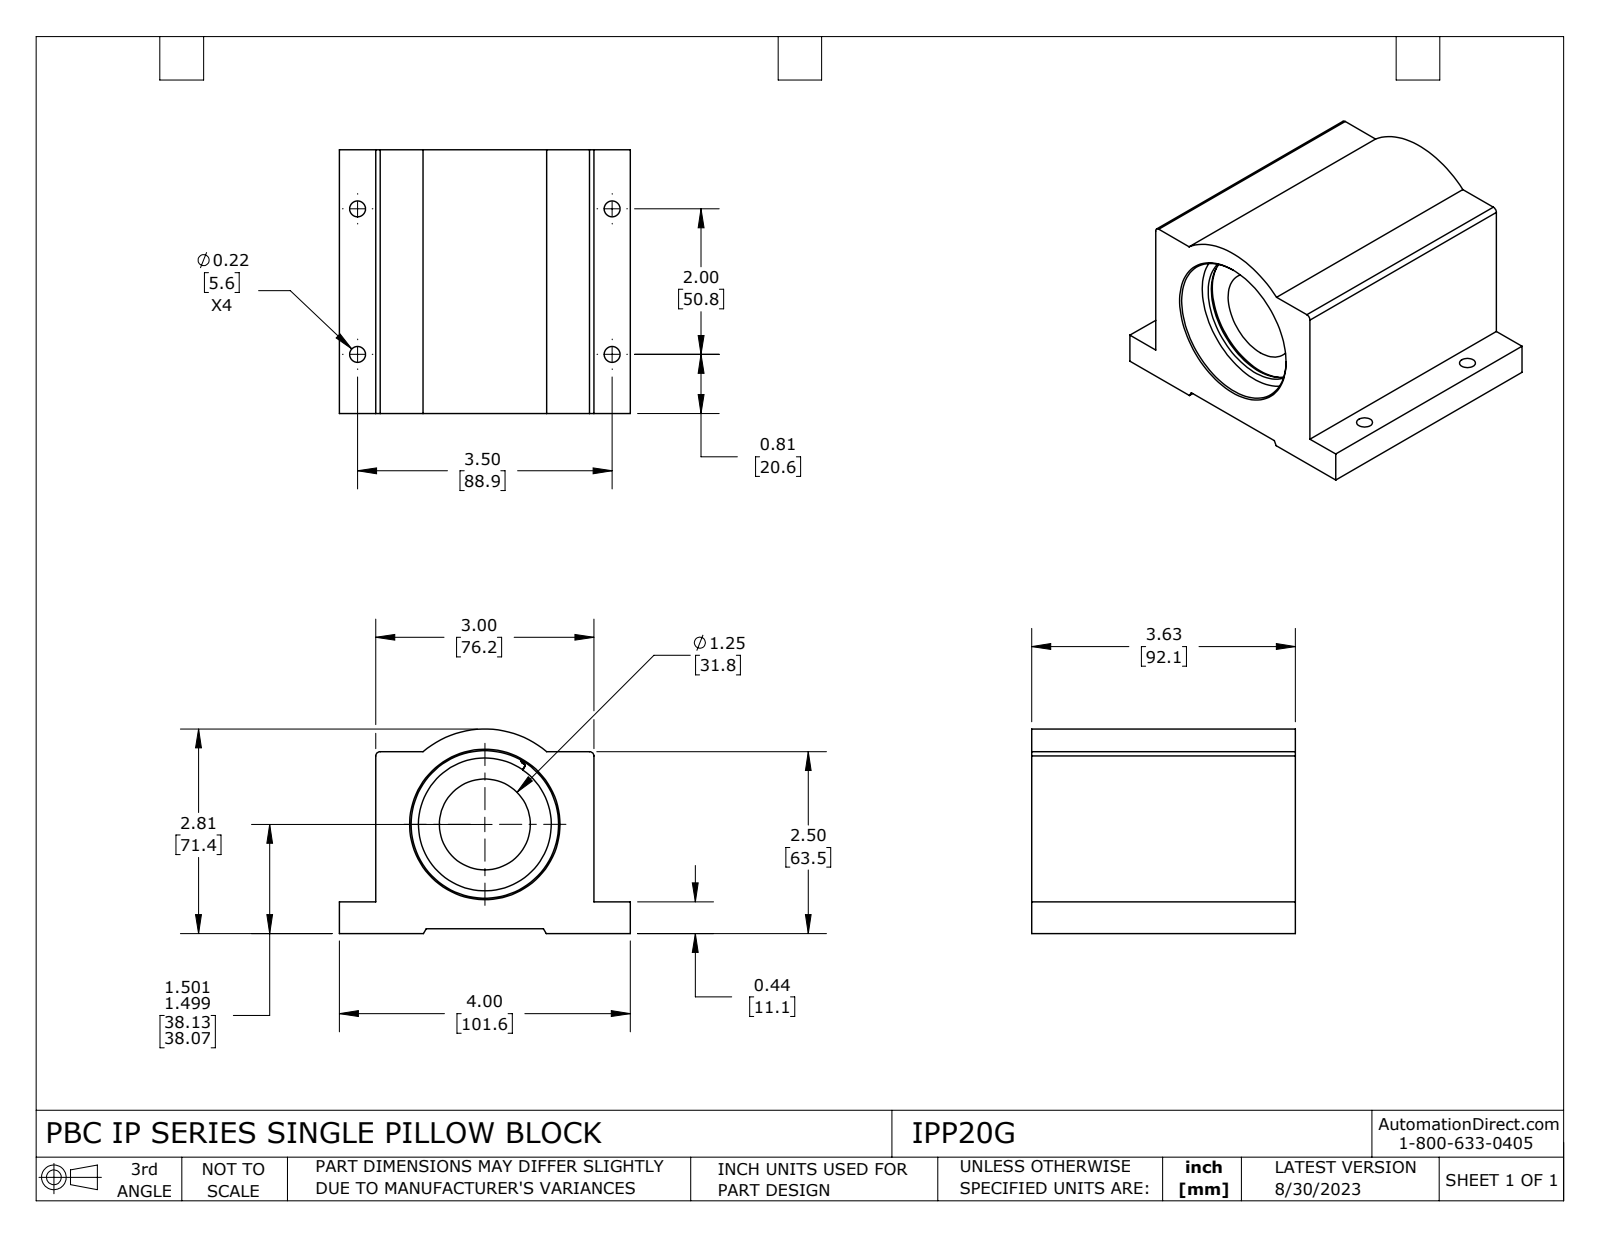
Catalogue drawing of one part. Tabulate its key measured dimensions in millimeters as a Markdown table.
| quantity | value |
| --- | --- |
| part name | IPP20G |
| STEP written by | SolidWorks 2021 (CONFIG_CONTROL_DESIGN) |
| units | millimeters |
| bodies | 4 solids, 126 faces (43 planar, 63 cylindrical, 20 other) |
| overall size | 101.6 × 92.1 × 71.4 |
| volume | 375 400 mm³ |
| surface area | 77 480 mm² |
| round holes (diameter × count) | 5.6 × 4, 31.8 × 1, 46.4 × 1, 47.3 × 1, 51.5 × 1, 53.9 × 1 |
| round bosses / shafts (diameter × count) | 54.4 × 1, 50.8 × 1, 47.9 × 1 |
| partial cylindrical surfaces (radius × count) | 0.7 × 4, 0.5 × 2, 0.8 × 2, 1.5 × 2, 33.3 × 1 |
| main face-to-face distances | 76.2, 1.7, 92.1, 63.5, 61.8, 12.7, 11.1, 9.4, 52.4, 88.9 |
| hole center spacings | 50.8, 88.9, 102.4 |
